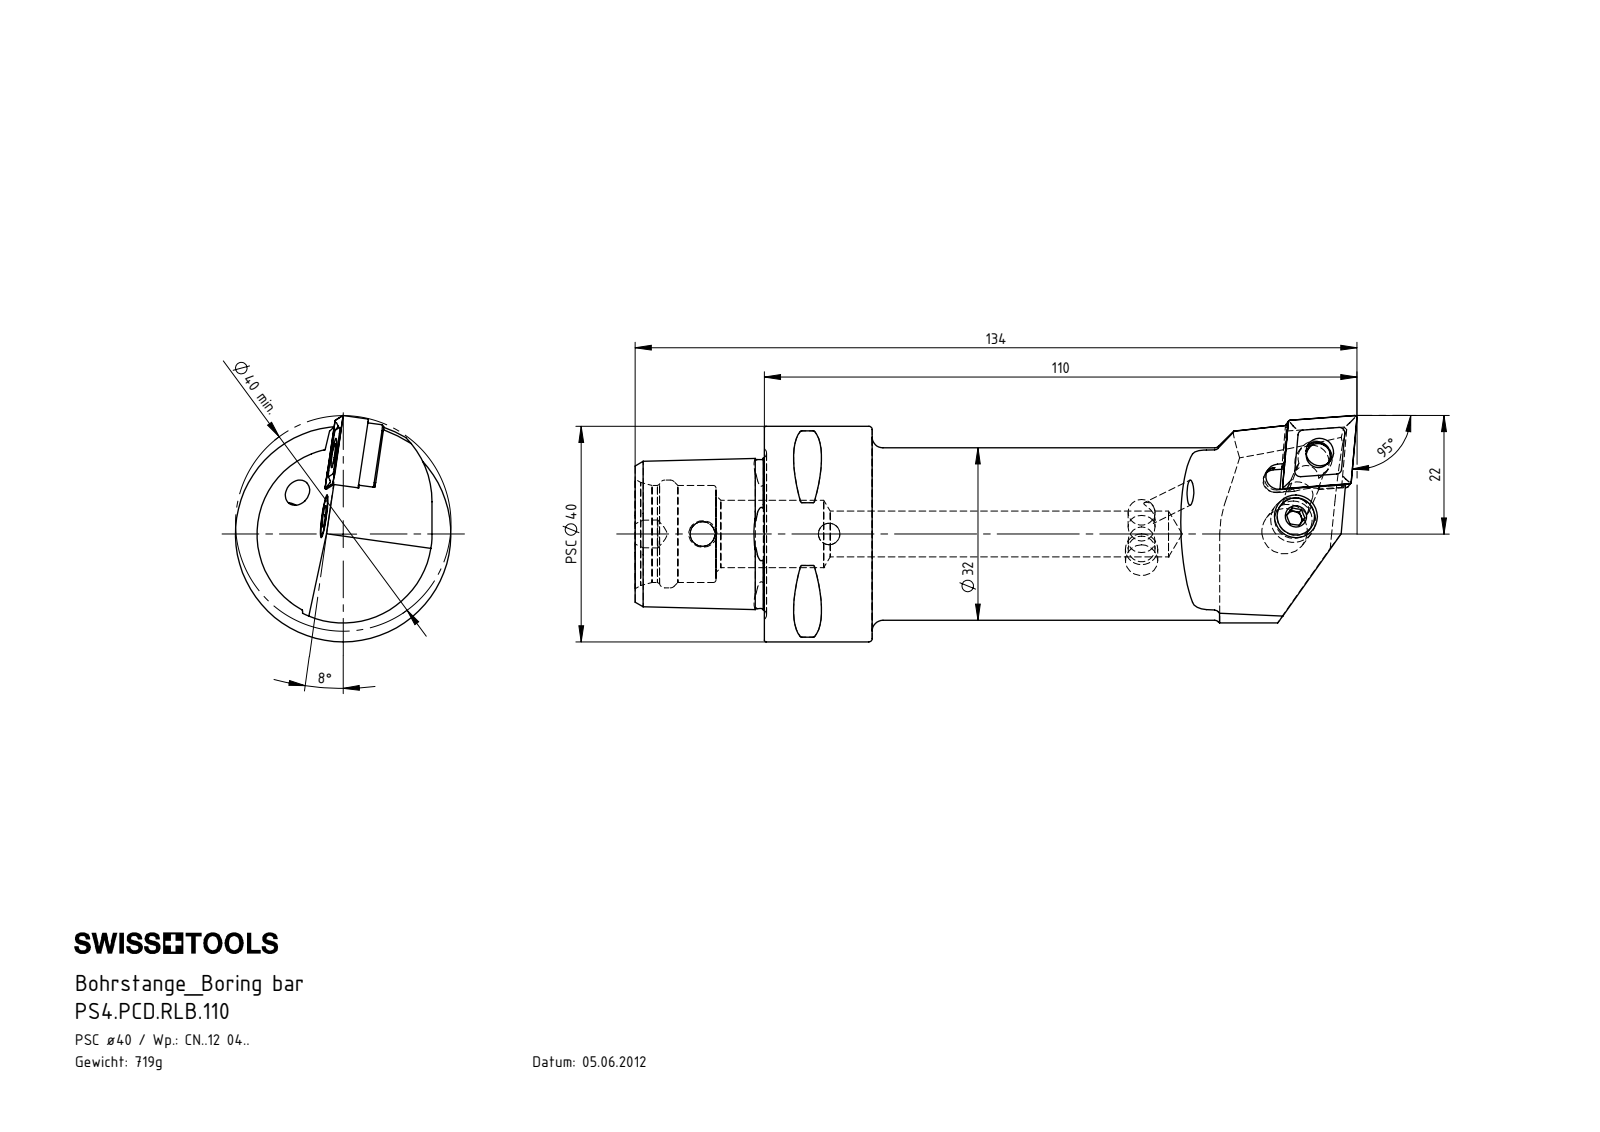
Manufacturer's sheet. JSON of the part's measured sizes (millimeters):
{"part_name": "PS4.PCD.RLB.110; KVT_MB_600_060; CNMG120404; PS4-PCD.RLB.110_A (+4 more)", "step_written_by": "SolidWorks 2017 (AUTOMOTIVE_DESIGN)", "units": "millimeters", "bodies": {"solids": 8, "faces": 366, "planar": 94, "cylindrical": 91, "other": 181}, "overall_size": [134, 42, 40], "volume_mm3": 90727, "surface_area_mm2": 22289, "round_holes": [[4, 1], [4.2, 1], [4.6, 1], [5, 1], [5.16, 1], [6.4, 1], [7, 1], [8.4, 1], [8.5, 1], [12.5, 1], [18, 1], [20, 1]], "round_bosses_or_shafts": [[40, 1], [32, 1], [8, 1], [7.9, 1], [6.4, 1], [6, 1], [4.5, 1], [3.55, 1]], "partial_cylinders_radius": [[0.3, 8], [0.4, 4], [1, 4], [2.5, 2], [3, 2], [2.1, 1], [2.2, 1], [2.35, 1]], "face_to_face_distances": [4.46, 20, 24, 44, 15.52, 0.5, 11.7, 3.19, 7.65, 4.83], "hole_center_spacings": [12.81, 12.87, 23.5]}
